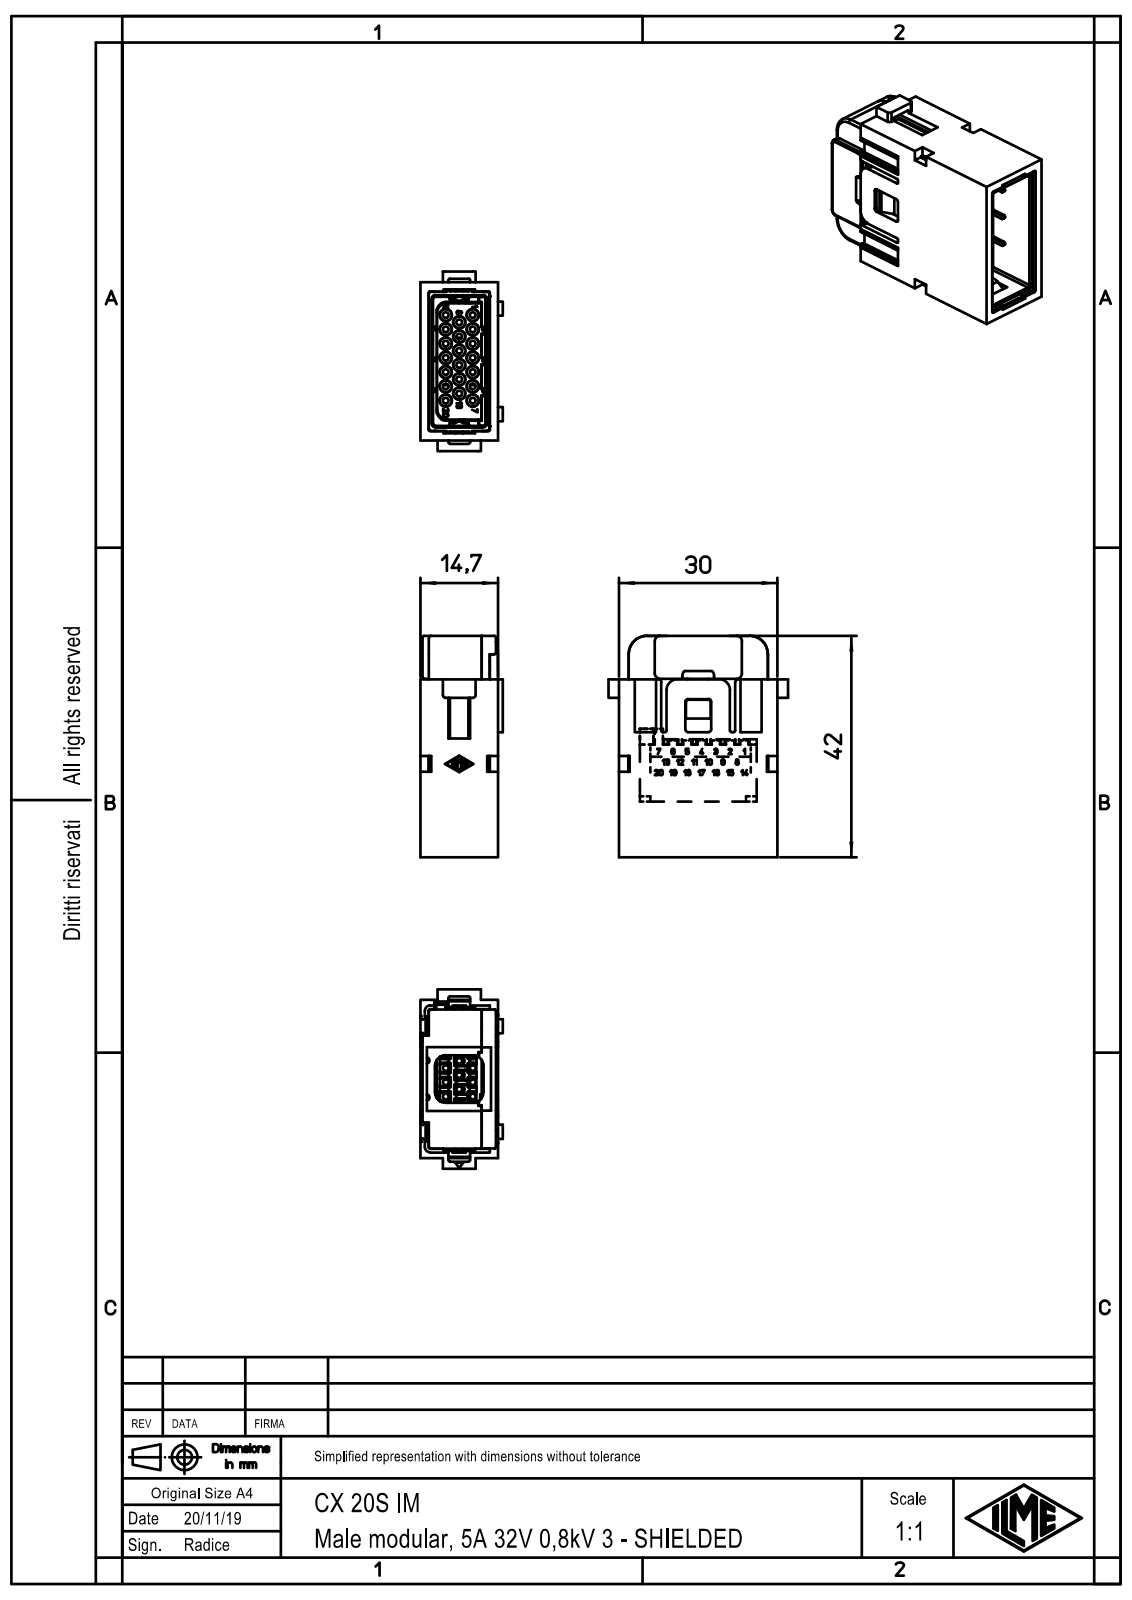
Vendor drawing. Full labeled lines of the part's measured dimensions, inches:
Part name (STEP PRODUCT): CX_20S_IM
STEP written by: Creo Elements/Direct Modeling 20.1B 02-Apr-2019 (C) Parametric Technology GmbH (AUTOMOTIVE_DESIGN)
Units: inches
Bodies: 1 solid, 423 faces (277 planar, 104 cylindrical, 42 other)
Overall size (bounding box): 1.652 × 1.339 × 0.614
Volume: 0.682 in³ · Surface area: 13.47 in²
Round holes (diameter × count): ⌀0.039 ×20, ⌀0.197 ×2
Round bosses / shafts (diameter × count): ⌀0.185 ×2
Partial cylindrical surfaces — rounded edges, fillets, slot ends (radius × count): R0.012 ×21, R0.02 ×11, R0.039 ×4, R0.016 ×2, R0.053 ×2, R0.059 ×2, R0.071 ×2, R0.073 ×2
Main face-to-face distances: 0.579, 0.122, 0.457, 0.094, 0.484, 0.028, 0.362, 1.181, 0.394, 0.516
Hole centre spacings: 0.114, 0.189, 0.106, 0.284, 0.213, 0.227, 0.385, 0.319
